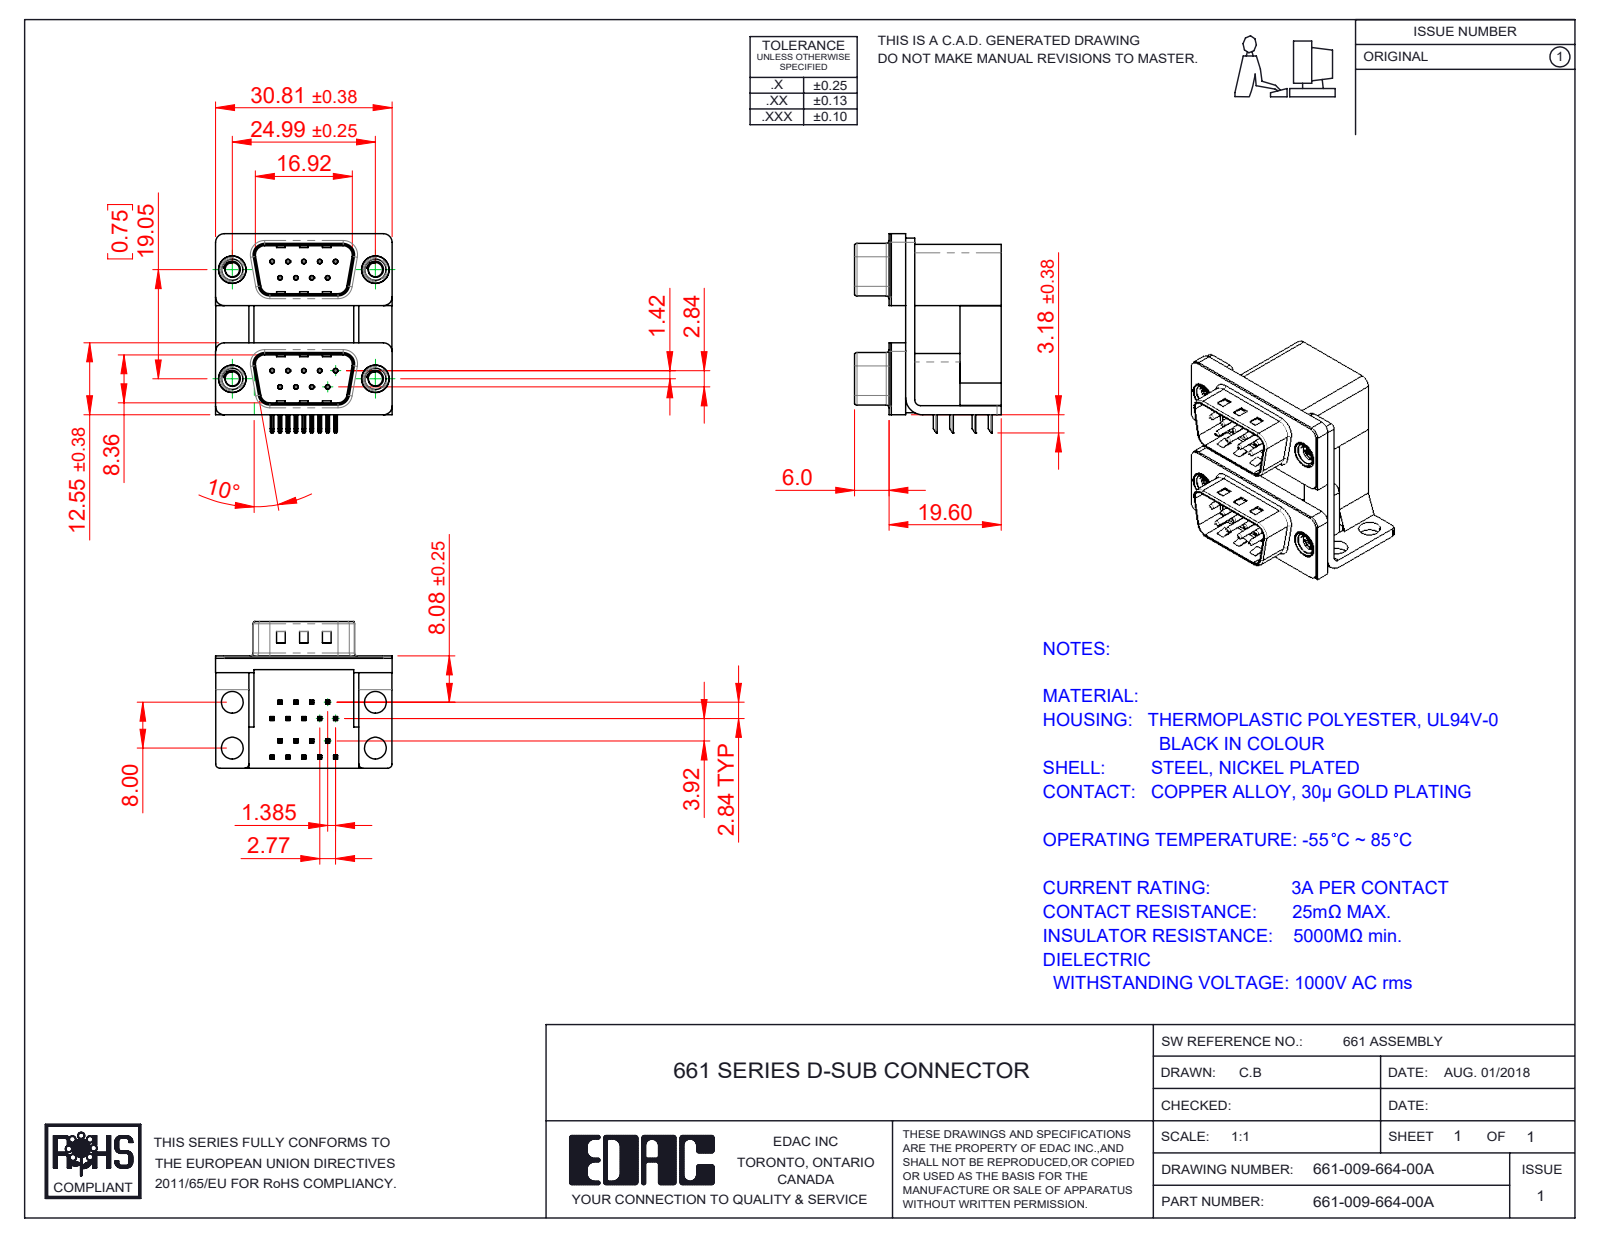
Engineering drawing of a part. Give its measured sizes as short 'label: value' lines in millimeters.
name: 661-009-664-00A; 661 Shell_09 Contacts; 661 Contact Bottom Lower; 661 Contact Top Lower (+7 more)
written by: SolidWorks 2020 (CONFIG_CONTROL_DESIGN)
unit: mm
bodies: 29 solids, 1952 faces (1152 planar, 602 cylindrical, 198 other)
size: 34.78 × 30.81 × 25.6
volume: 10 256 mm³; area: 11 786 mm²
holes: 18× ⌀0.35, 18× ⌀0.8, 4× ⌀2.5, 4× ⌀3.5, 4× ⌀3.8, 4× ⌀4, 4× ⌀4.8, 4× ⌀5
bosses: 18× ⌀0.75, 4× ⌀4.9, 4× ⌀4.75, 4× ⌀3.9
rounds: 72× R0.25, 36× R0.12, 16× R0.5, 14× R1.5, 8× R0.75, 8× R0.9, 8× R1.6, 8× R2
face distances: 0.4, 2.5, 19.05, 16.7, 19.2, 7.2, 10.69, 9.5, 12, 1.6
hole spacings: 3.16, 2.77, 19.25, 19.05, 5.54, 19.84, 16.27, 21.93
